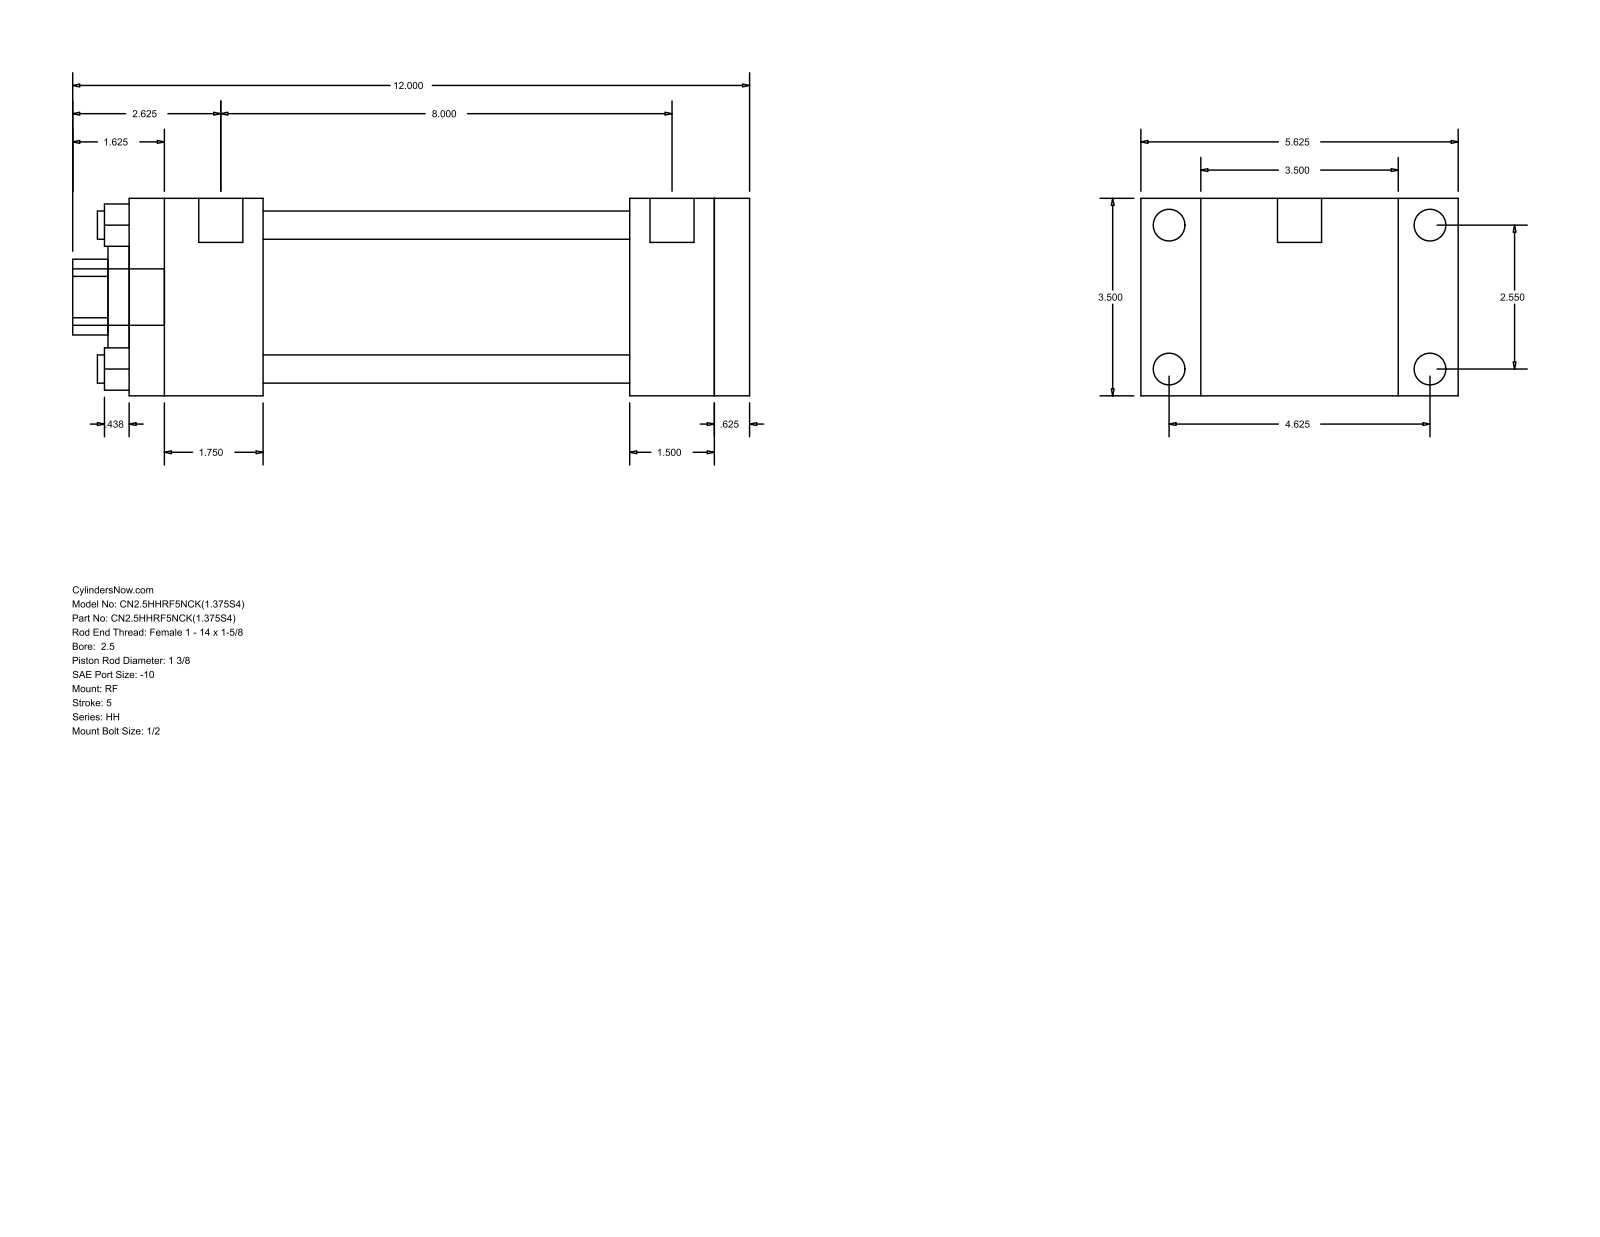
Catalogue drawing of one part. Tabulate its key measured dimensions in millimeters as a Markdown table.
| quantity | value |
| --- | --- |
| part name | HH_RF__0250_1.375 |
| STEP written by | GSSL Pune (CONFIG_CONTROL_DESIGN) |
| units | millimeters |
| bodies | 0 solids, 92 faces (64 planar, 28 cylindrical, 0 other) |
| overall size | 304.8 × 142.88 × 88.9 |
| round holes (diameter × count) | 12.7 × 4, 34.92 × 1, 50.8 × 1, 73.03 × 1 |
| round bosses / shafts (diameter × count) | 14.3 × 4, 5.56 × 4, 19.84 × 2, 25.4 × 1 |
| partial cylindrical surfaces (radius × count) | 17.06 × 1 |
| main face-to-face distances | 88.9, 15.87, 263.53, 279.4, 60.32, 203.21, 219.08, 225.42, 165.1, 38.11 |
| hole center spacings | 45.79, 64.76, 91.58 |
